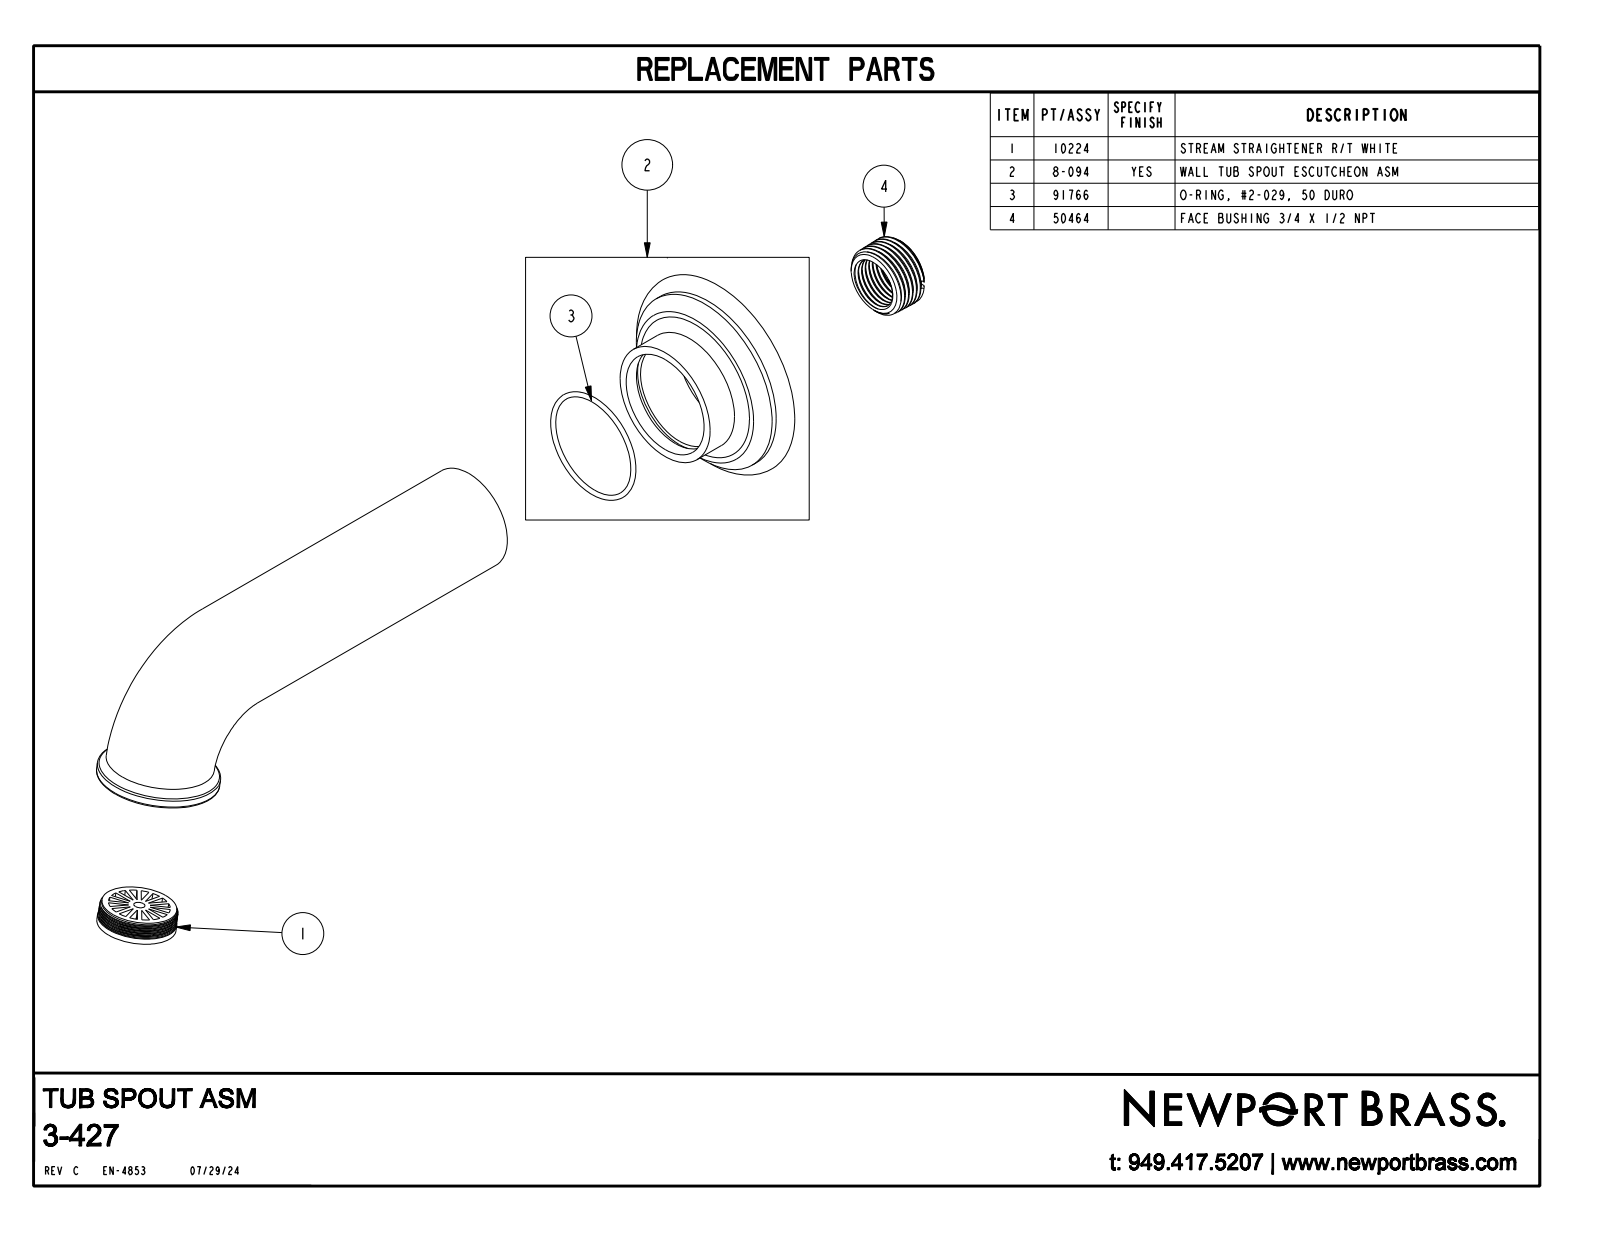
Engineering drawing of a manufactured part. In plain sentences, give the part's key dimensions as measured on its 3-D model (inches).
The part is named "80224; 8-093_ASM; 80241; 8-094_ASM (+1 more)". Its 3-D file was written by "CREO PARAMETRIC BY PTC INC, 2018400 (AUTOMOTIVE_DESIGN)". It is 2 solids with 30 faces: 6 planar, 10 cylindrical and 14 other. Overall it measures 6.911 by 3.019 by 3 inches. Its volume is 16.04 cubic inches and its surface area 55.79 square inches. Round bosses or shafts: 1 of diameter 2.64, 1 of diameter 2.5, 1 of diameter 1.75, 1 of diameter 1.71, 1 of diameter 1.5. The main face-to-face distances are 1.03, 1.02, 0.03, 0.02, 1, 0.45, 0.44, 0.42, 0.58.
